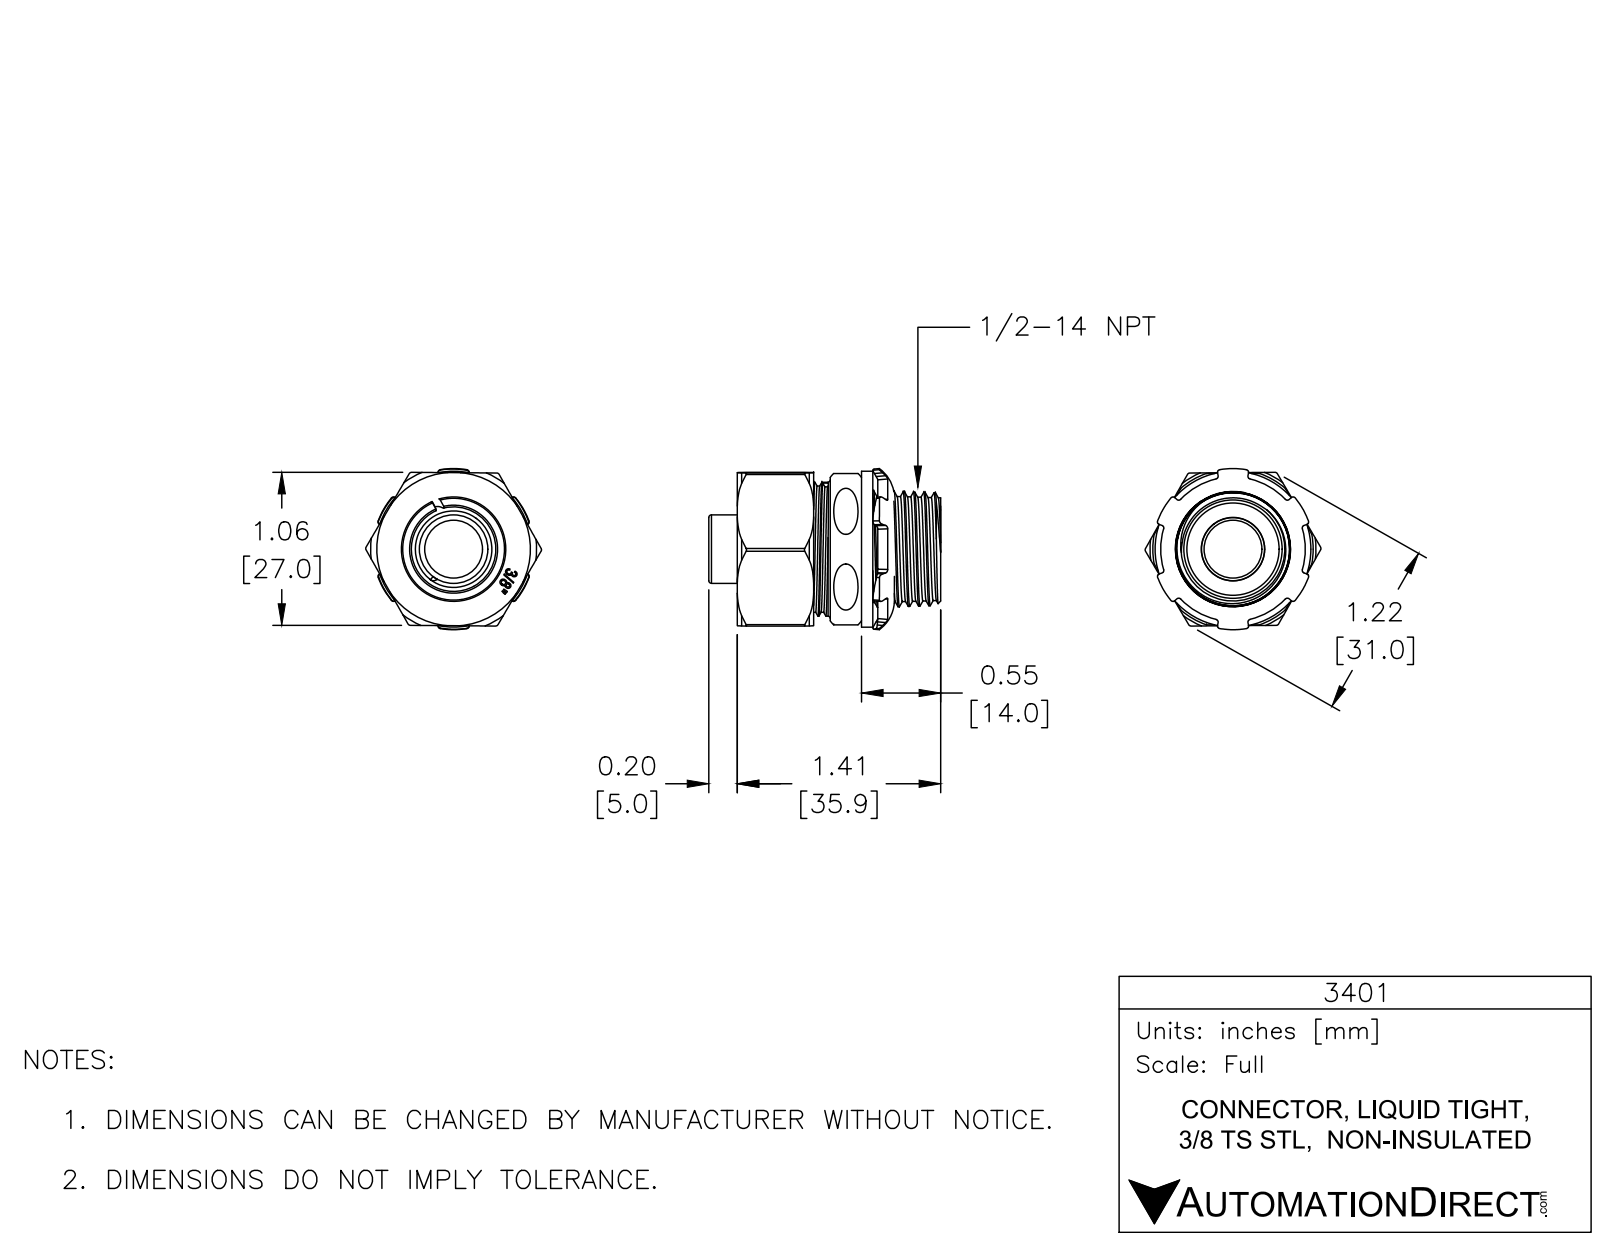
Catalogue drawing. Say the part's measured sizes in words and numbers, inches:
The part is named "3401-3; 3401-2; 3401-6; 3401-1 (+3 more)". Its 3-D file was written by "SolidWorks 2017 (AUTOMOTIVE_DESIGN)". It is 6 solids with 646 faces: 220 planar, 96 cylindrical and 330 other. Overall it measures 1.611 by 1.221 by 1.119 inches. Its volume is 0.517 cubic inches and its surface area 21.73 square inches. Round holes: 1 of diameter 0.1, 1 of diameter 0.402, 1 of diameter 0.44, 1 of diameter 0.728, 1 of diameter 0.732, 1 of diameter 0.787, 1 of diameter 0.858, 1 of diameter 0.906. Round bosses or shafts: 1 of diameter 1.083, 1 of diameter 0.93, 1 of diameter 0.866, 1 of diameter 0.768, 1 of diameter 0.476, 1 of diameter 0.438, 1 of diameter 0.081. Partial cylindrical surfaces (rounded edges, fillets, slot ends): 8 of radius 0.006, 6 of radius 0.02, 2 of radius 0.034, 1 of radius 0.008, 1 of radius 0.013, 1 of radius 0.334. The main face-to-face distances are 1.063, 0.863, 0.942, 0.079, 1.063, 0.531, 0.332, 0.411, 0.071, 0.792. The hole center spacings are 0.453.
